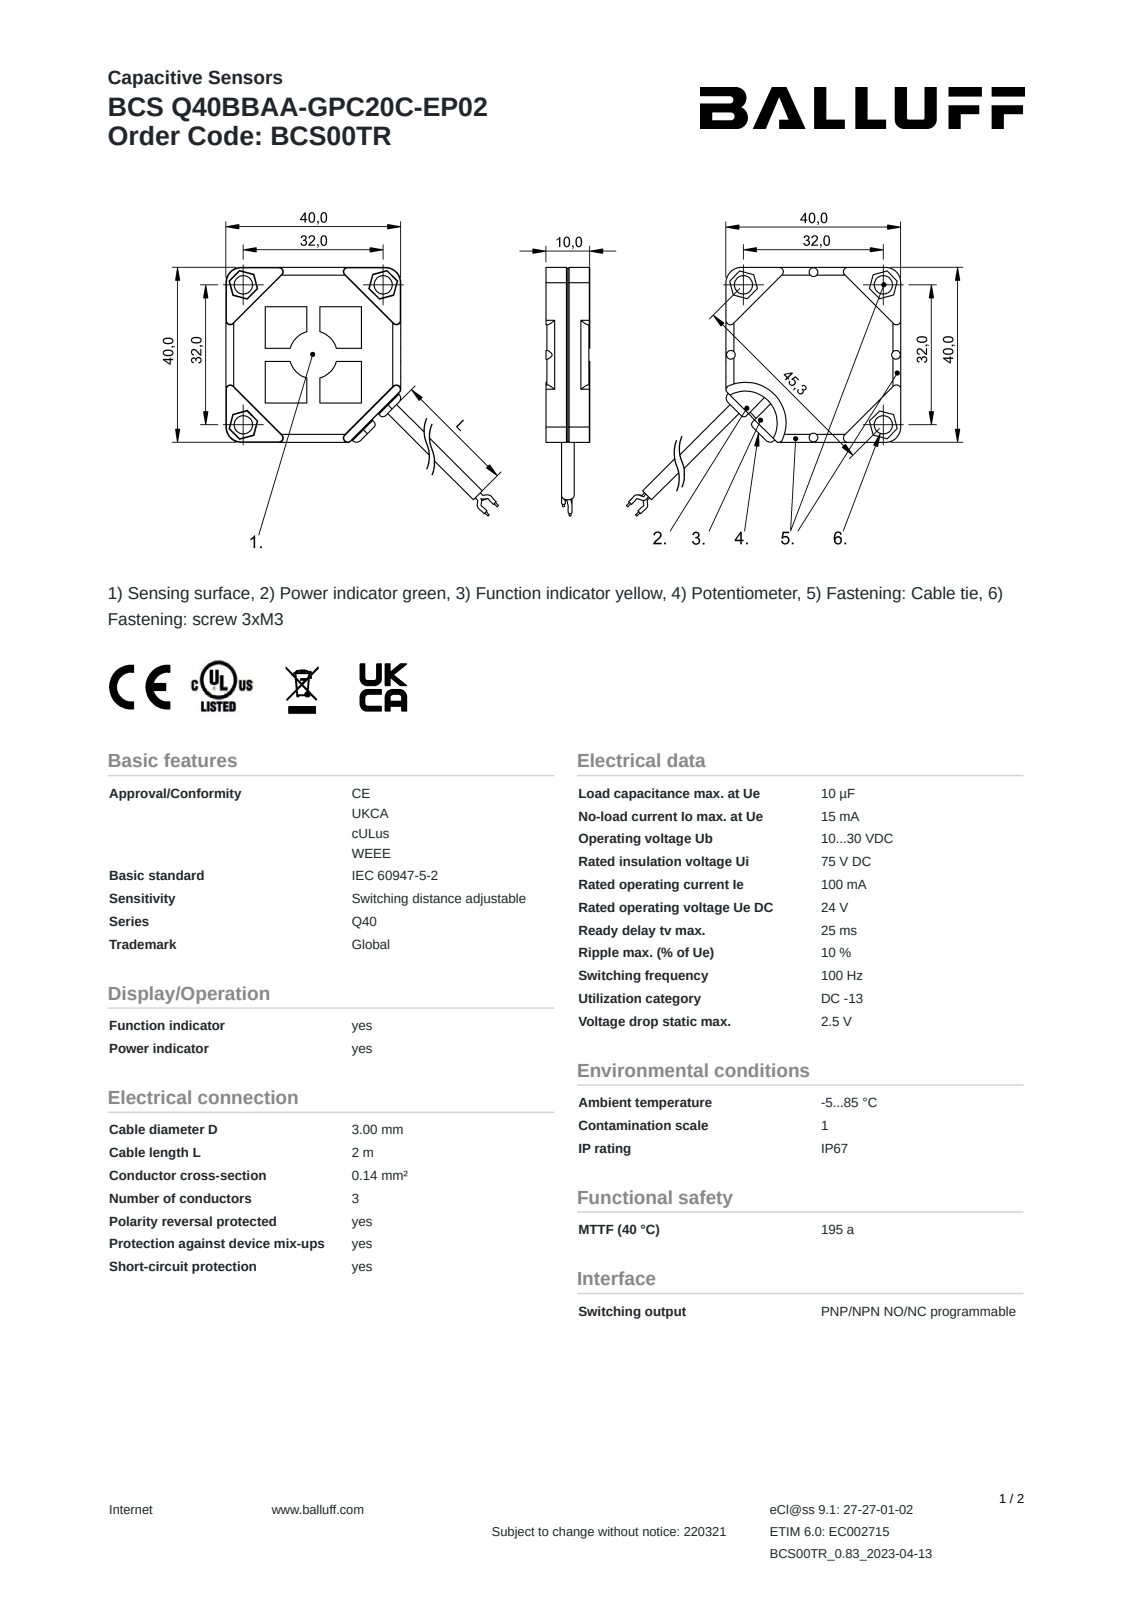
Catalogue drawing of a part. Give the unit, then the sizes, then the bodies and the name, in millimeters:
Units: millimetres
Overall size (bounding box): 45.6 × 40.5 × 10
Round holes (diameter × count): ⌀4.2 ×3, ⌀3.2 ×2
Round bosses / shafts (diameter × count): ⌀2 ×4, ⌀3 ×1
Partial cylindrical surfaces — rounded edges, fillets, slot ends (radius × count): R1 ×8, R0.5 ×6, R3.5 ×3, R3 ×2, R5.5 ×1, R7.3 ×1, R9.3 ×1
Main face-to-face distances: 9.8, 9.6, 40, 10, 32.5, 5.7, 2, 8, 1.8, 7.8
Hole centre spacings: 32, 7.4, 45.2
Volume: 14 300 mm³ · Surface area: 5 119 mm²
Bodies: 1 solid, 178 faces (126 planar, 46 cylindrical, 6 other)
Part name (STEP PRODUCT): BCS00TR
STEP written by: SolidWorks 2021 (AUTOMOTIVE_DESIGN)
